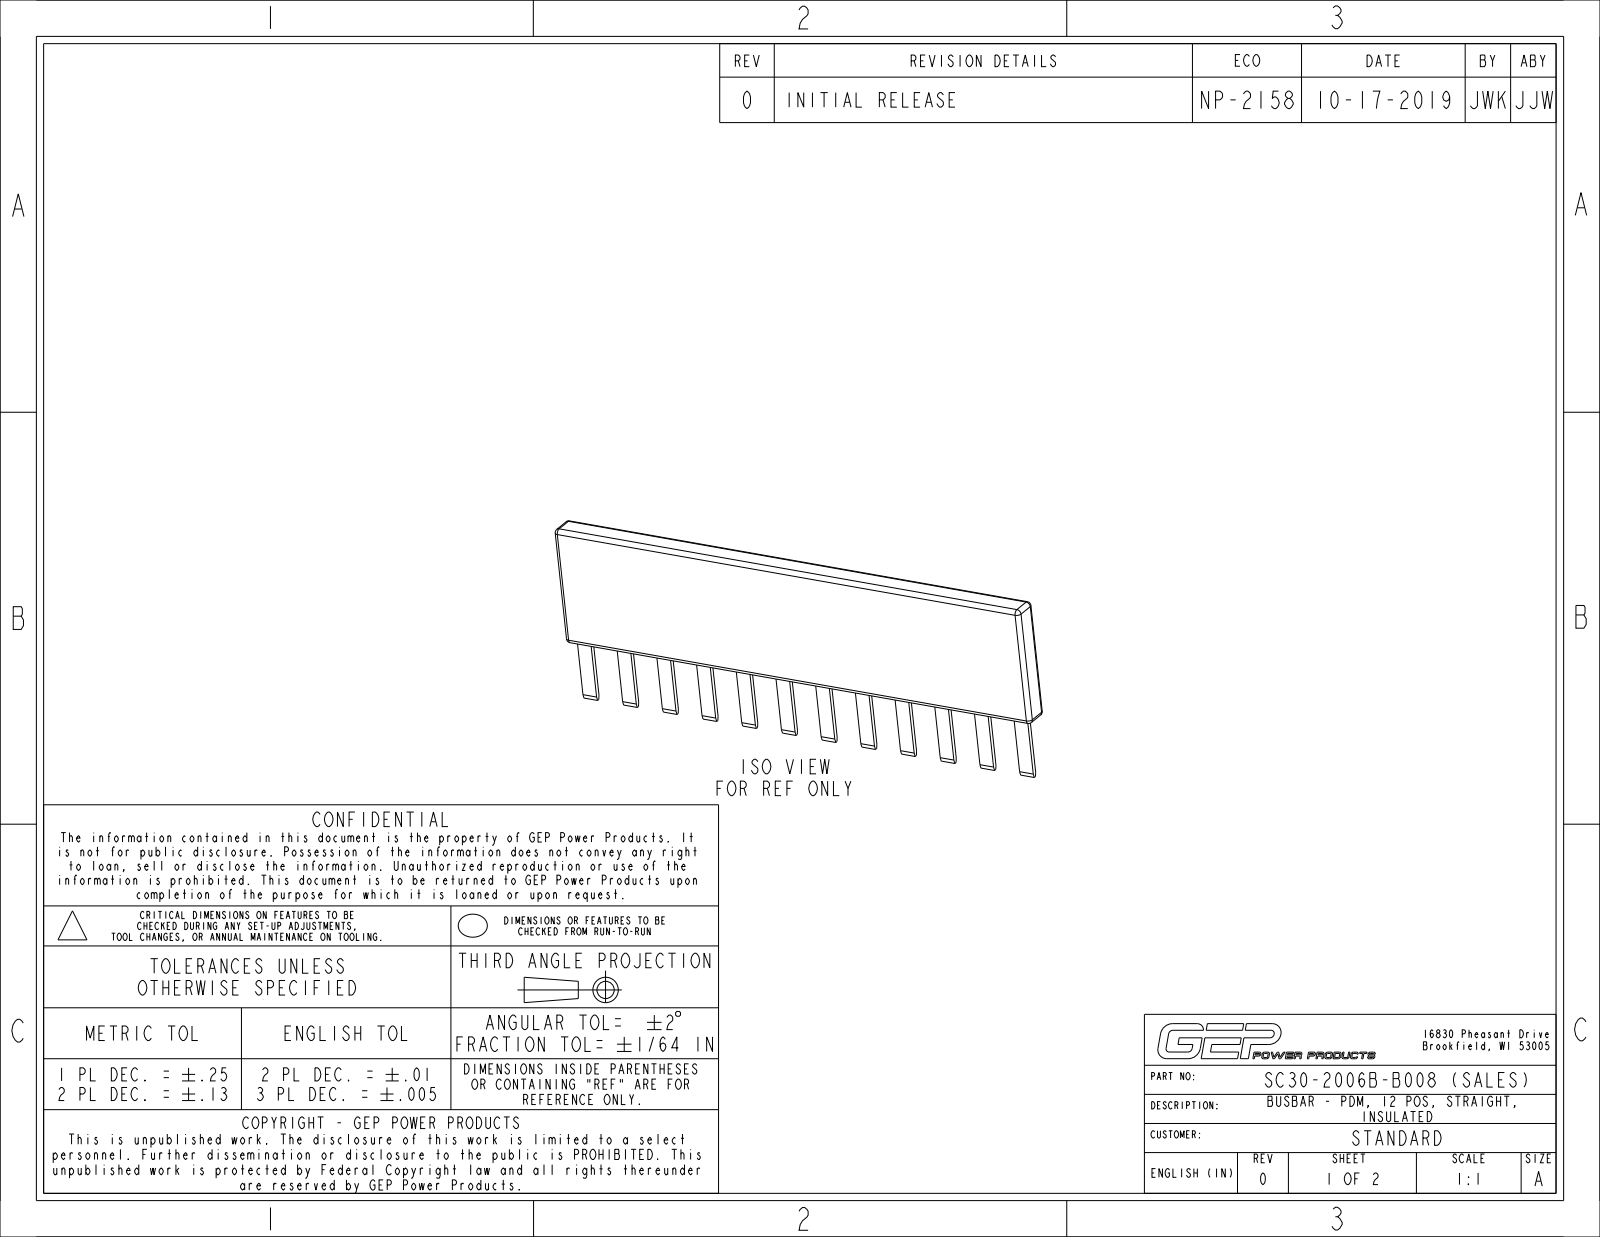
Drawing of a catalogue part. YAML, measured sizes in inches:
part_name: "PC29-2004B-C000_MOLD; PC29-2004B-C000_NCF; PC30-2006B-B008_NCF_ASM; SC30-2006B-B008_NCF_ASM"
step_written_by: "CREO PARAMETRIC BY PTC INC, 2017110 (CONFIG_CONTROL_DESIGN)"
units: inches
bodies: {solids: 2, faces: 165, planar: 143, cylindrical: 14, other: 8}
overall_size: [3.75, 1.31, 0.184]
volume: 0.615
surface_area: 26.74
partial_cylinders:
  - {radius: 0.03, count: 12}
  - {radius: 0.032, count: 1}
face_to_face_distances: [0.06, 0.124, 0.032, 0.032, 0.064, 0.092, 0.184, 0.092, 0.87, 0.061]
